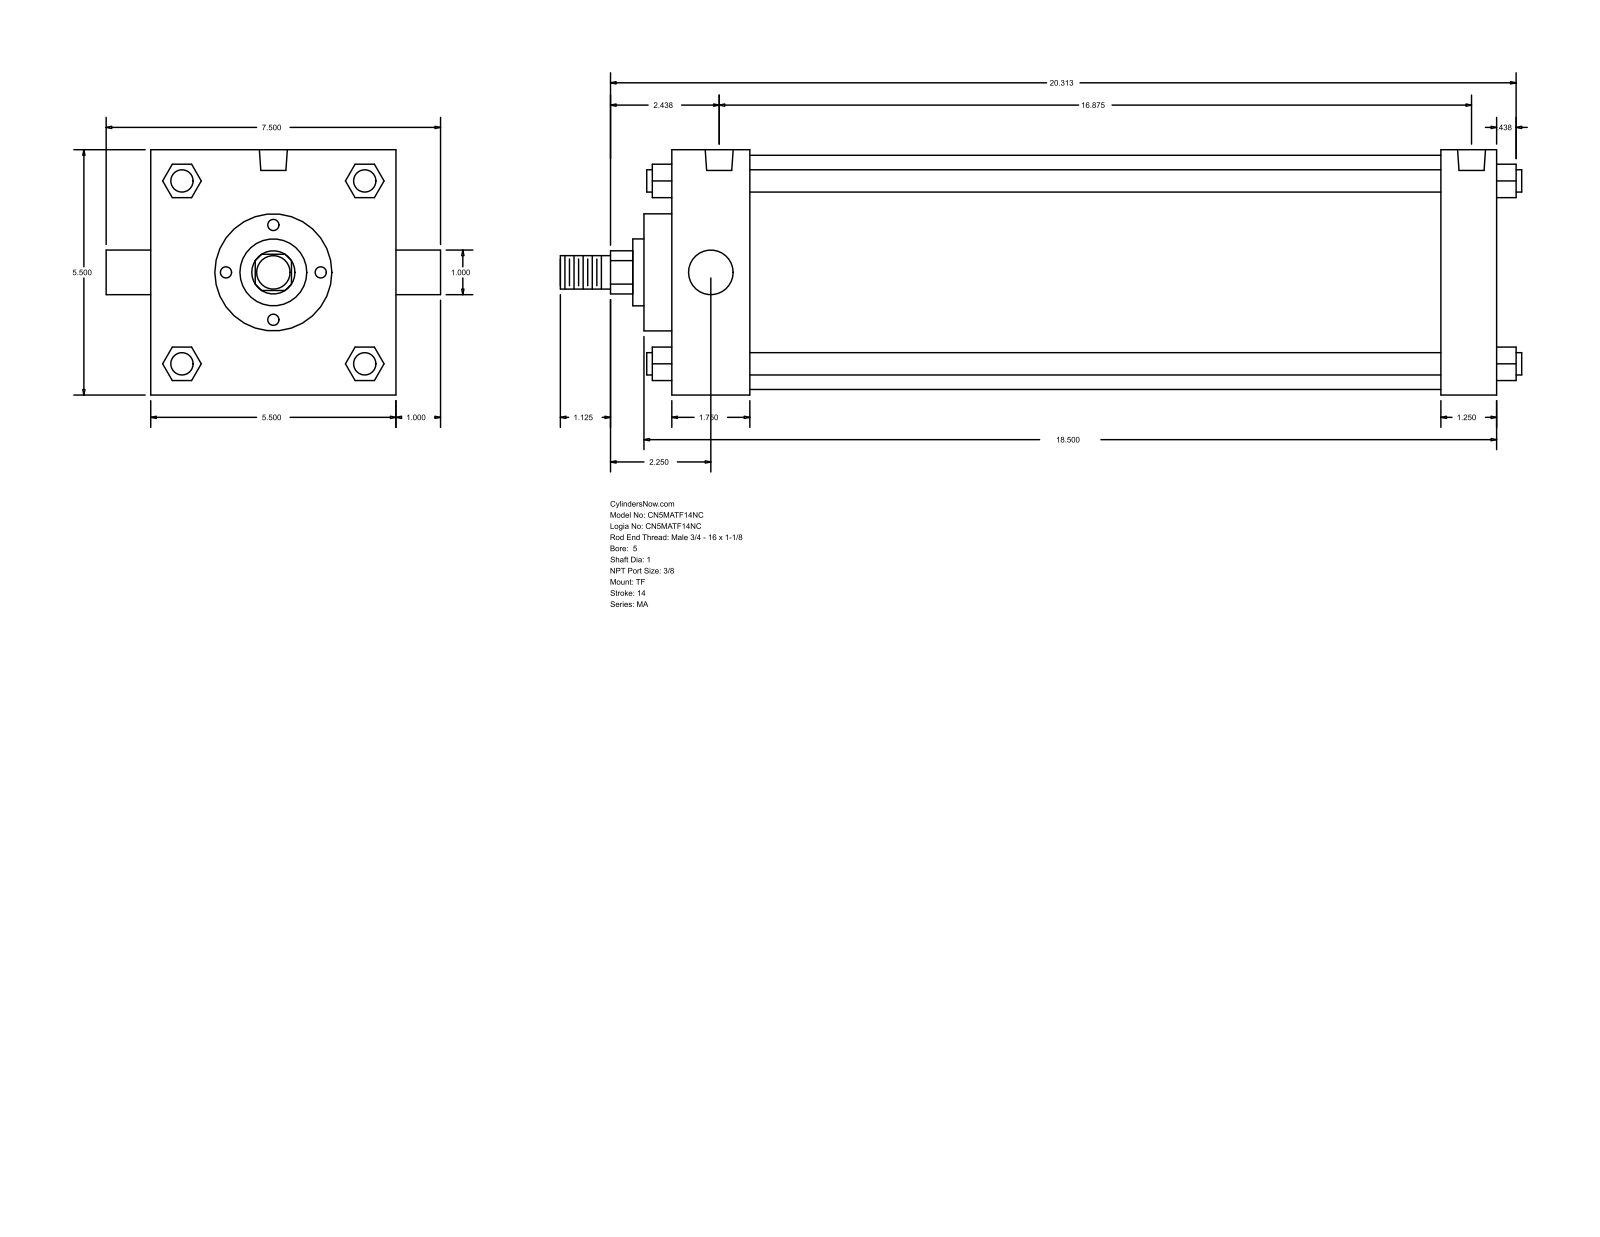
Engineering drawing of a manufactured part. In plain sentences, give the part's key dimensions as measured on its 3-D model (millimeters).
The part is named "MA_TF__0500_1". Its 3-D file was written by "GSSL Pune (CONFIG_CONTROL_DESIGN)". It is 0 solids with 122 faces: 93 planar, 29 cylindrical and 0 other. Overall it measures 547.69 by 190.5 by 139.7 millimeters. Round holes: 3 of diameter 11.11, 2 of diameter 15.93. Round bosses or shafts: 4 of diameter 12.7, 2 of diameter 25.4, 1 of diameter 133.35, 1 of diameter 66.67, 1 of diameter 38.1, 1 of diameter 19.05. Partial cylindrical surfaces (rounded edges, fillets, slot ends): 1 of radius 12.29. The main face-to-face distances are 139.7, 469.9, 438.15, 31.75, 44.46, 393.69, 425.44, 15.87, 60.33, 454.02. The hole center spacings are 4.76, 4.77, 419.1, 423.86, 423.87, 428.63.
